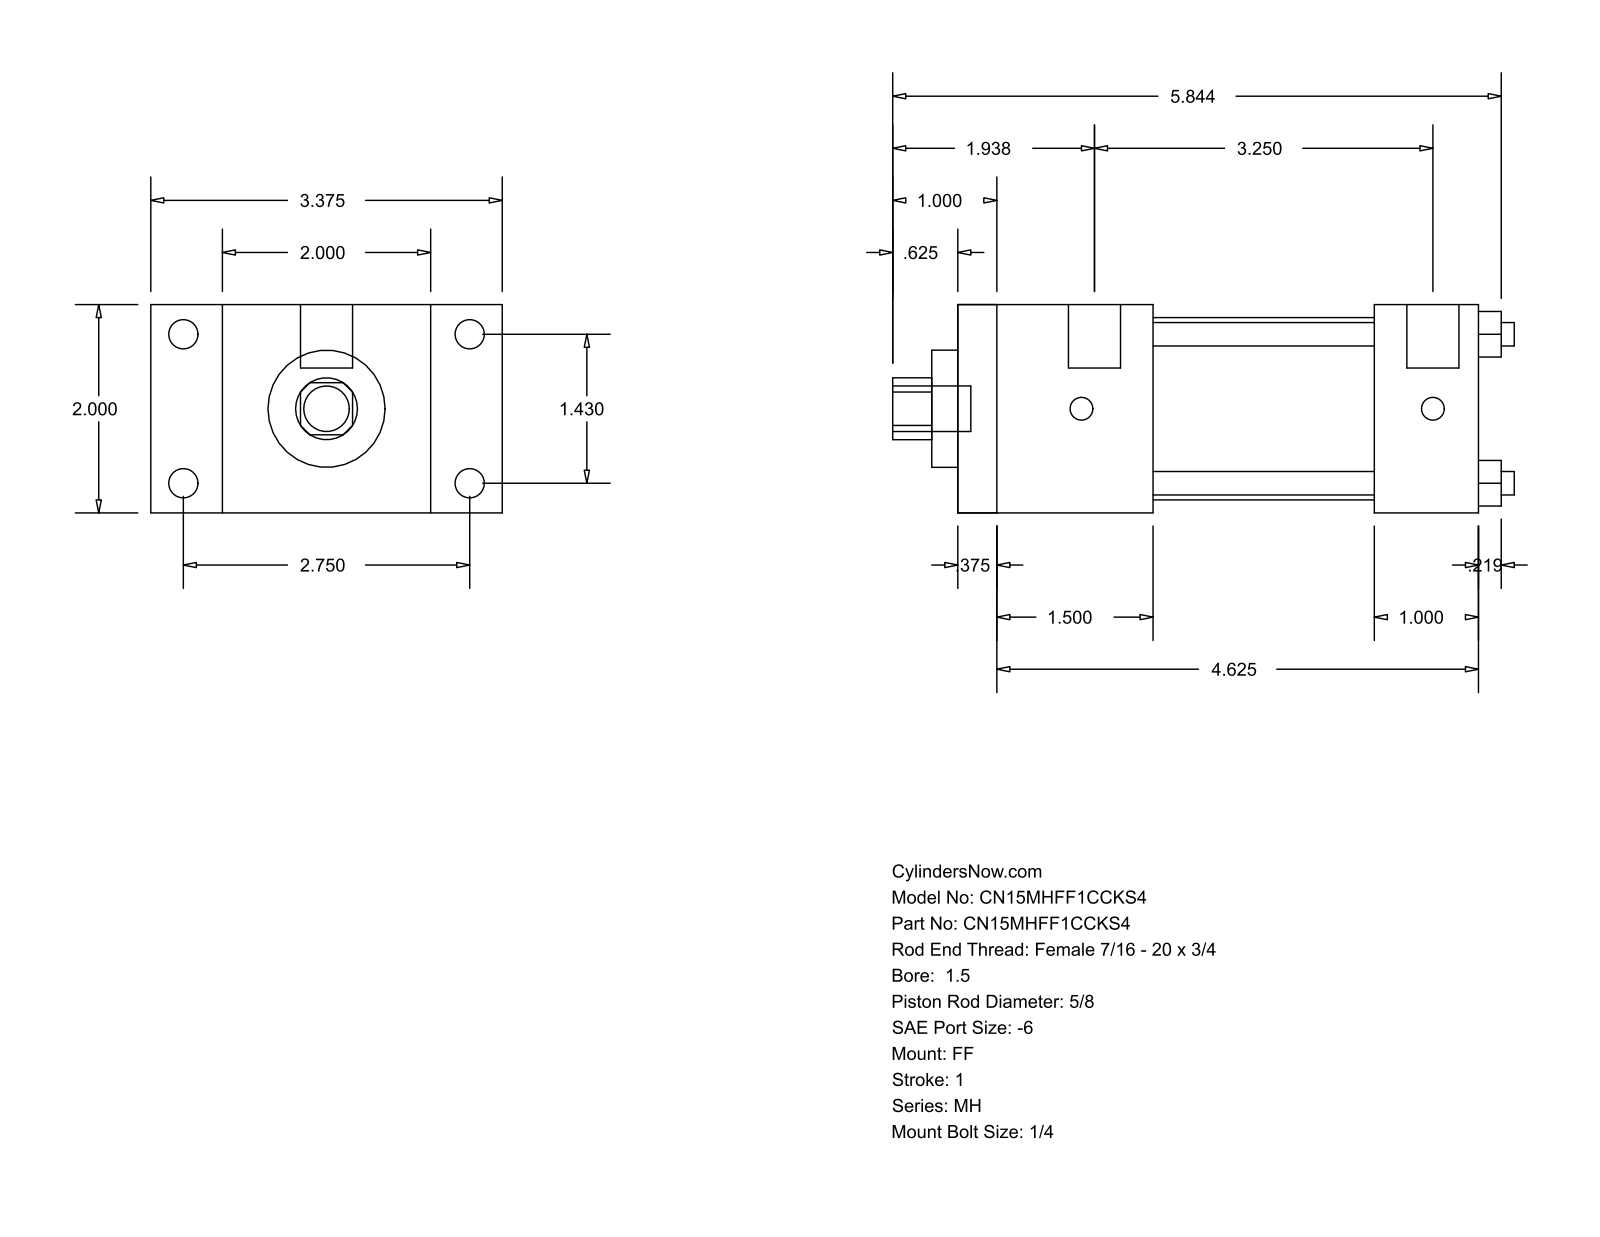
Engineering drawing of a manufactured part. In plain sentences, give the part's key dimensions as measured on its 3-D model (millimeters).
The part is named "MH_FF__0150_0.625". Its 3-D file was written by "GSSL Pune (CONFIG_CONTROL_DESIGN)". It is 0 solids with 92 faces: 64 planar, 28 cylindrical and 0 other. Overall it measures 151.61 by 85.72 by 50.8 millimeters. Round holes: 4 of diameter 5.71, 1 of diameter 15.88, 1 of diameter 28.57, 1 of diameter 44.45. Round bosses or shafts: 4 of diameter 7.14, 4 of diameter 5.56, 2 of diameter 12.7, 1 of diameter 11.11. Partial cylindrical surfaces (rounded edges, fillets, slot ends): 1 of radius 7.54. The main face-to-face distances are 50.8, 127, 9.52, 117.48, 53.97, 17.46, 68.26, 47.62, 38.1, 79.38. The hole center spacings are 25.68, 36.32, 51.36.
